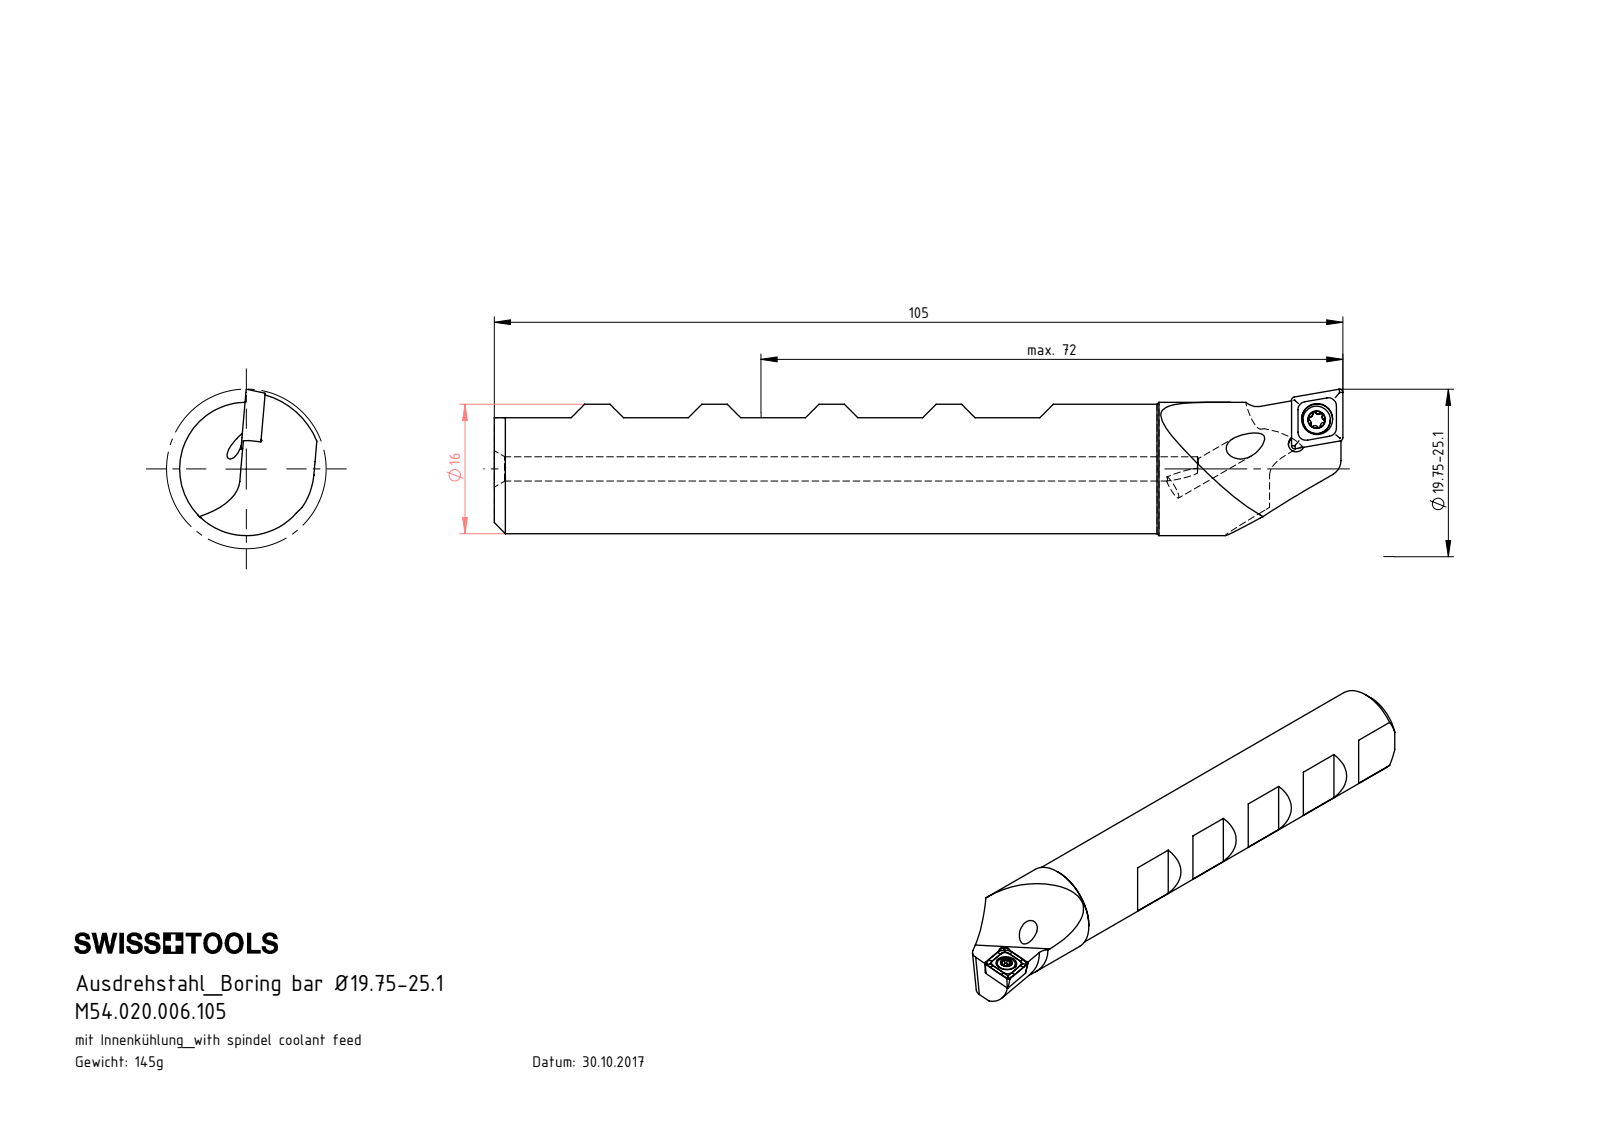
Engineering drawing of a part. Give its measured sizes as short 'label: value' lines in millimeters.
name: CCMT060204; WCA-ER2.001.006_A; B20-WCA.K11.105_B; B20.WCA.K11.105
written by: SolidWorks 2017 (AUTOMOTIVE_DESIGN)
unit: mm
bodies: 3 solids, 109 faces (42 planar, 26 cylindrical, 41 other)
size: 105 × 18.12 × 16.98
volume: 18 365 mm³; area: 6 522 mm²
holes: 2× ⌀3, 1× ⌀2, 1× ⌀2.05, 1× ⌀2.8, 1× ⌀3.85
bosses: 1× ⌀16.5, 1× ⌀16, 1× ⌀3.4, 1× ⌀2.5
rounds: 6× R0.21, 5× R0.36, 1× R0.36, 1× R2, 1× R8.4, 1× R9.5, 1× R10
face distances: 10.25, 20.5, 2.18, 20.51, 30.76, 6.88, 9.06, 30.75, 10.26, 41.01
hole spacings: 3.89, 4
